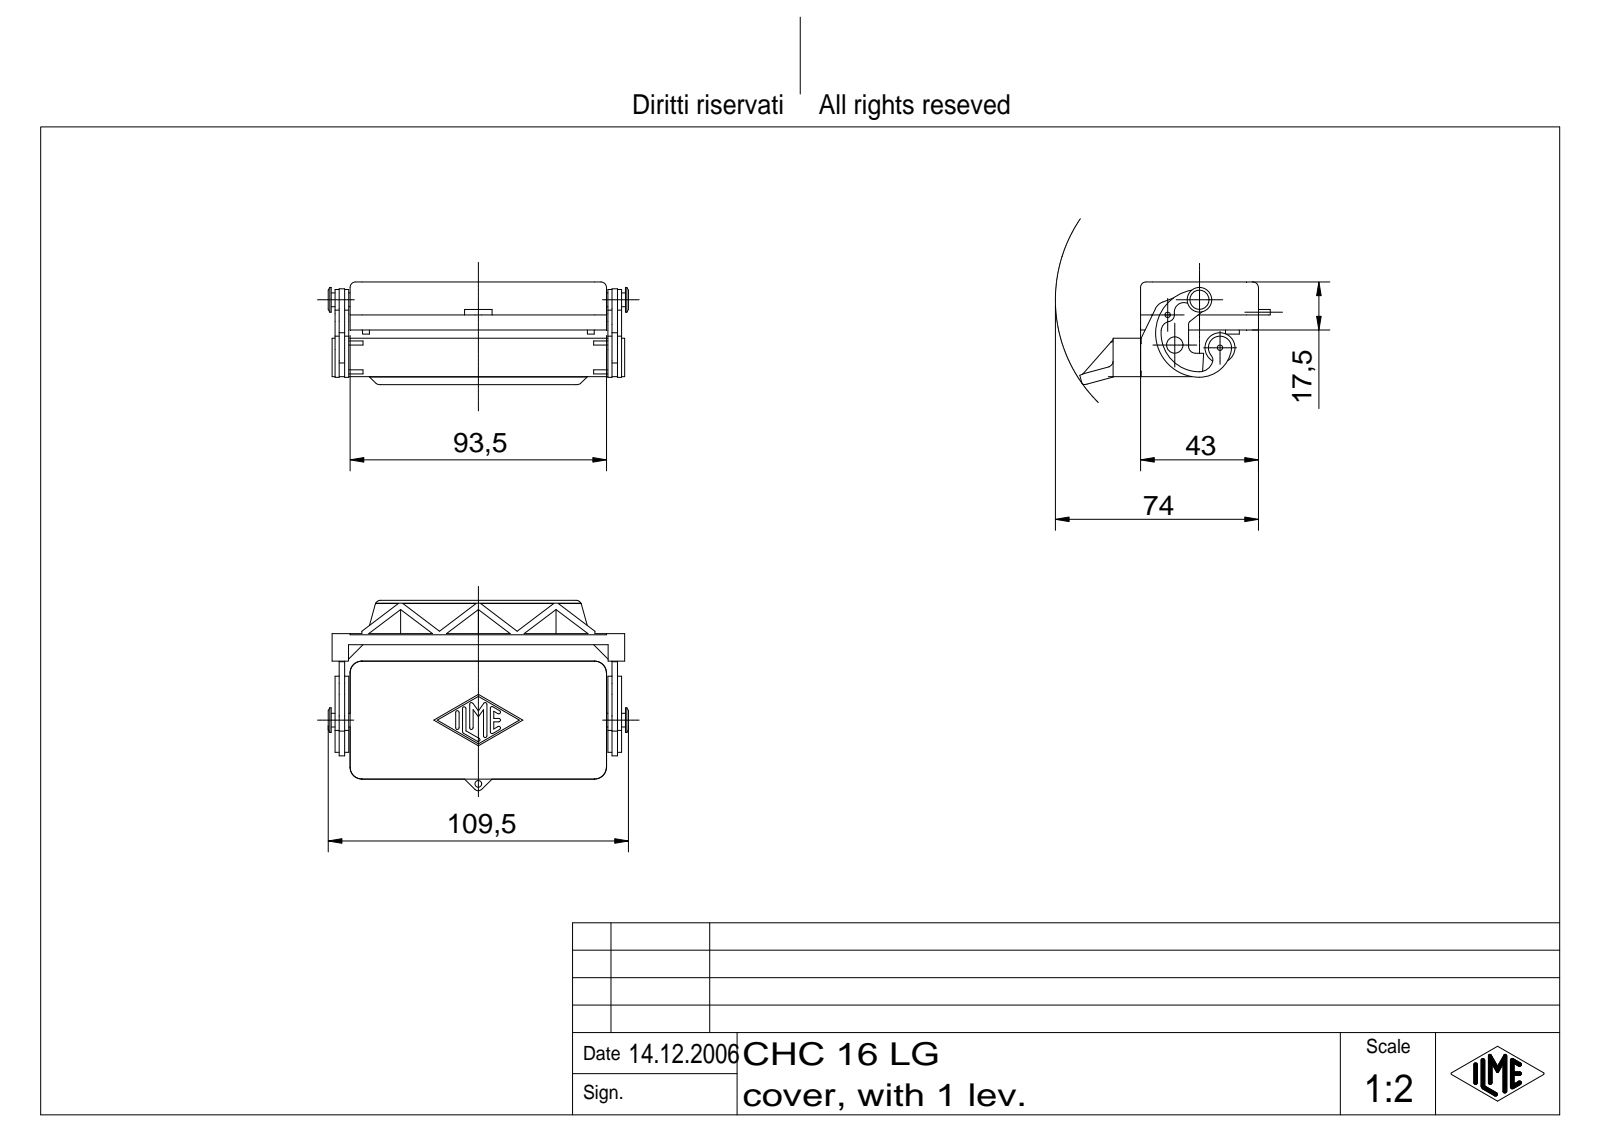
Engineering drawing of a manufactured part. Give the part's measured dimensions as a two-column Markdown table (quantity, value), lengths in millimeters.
| quantity | value |
| --- | --- |
| part name | CHC 16 LG |
| STEP written by | Autodesk Inventor 7 (AUTOMOTIVE_DESIGN) |
| units | millimeters |
| bodies | 1 solid, 374 faces (151 planar, 123 cylindrical, 100 other) |
| overall size | 109.5 × 69.45 × 37.43 |
| volume | 45 005 mm³ |
| surface area | 28 461 mm² |
| round holes (diameter × count) | 2 × 2, 2.5 × 2, 6 × 1 |
| round bosses / shafts (diameter × count) | 11 × 1, 9 × 1, 5 × 1 |
| partial cylindrical surfaces (radius × count) | 2 × 17, 0.62 × 14, 4.3 × 6, 1 × 3, 2.5 × 3, 3.5 × 2, 5 × 2, 1.5 × 1 |
| main face-to-face distances | 3, 4.5, 14.5, 38.5, 17.5, 4, 49, 10.5, 2, 10 |
| hole center spacings | 11.3, 16.53, 22.56 |
